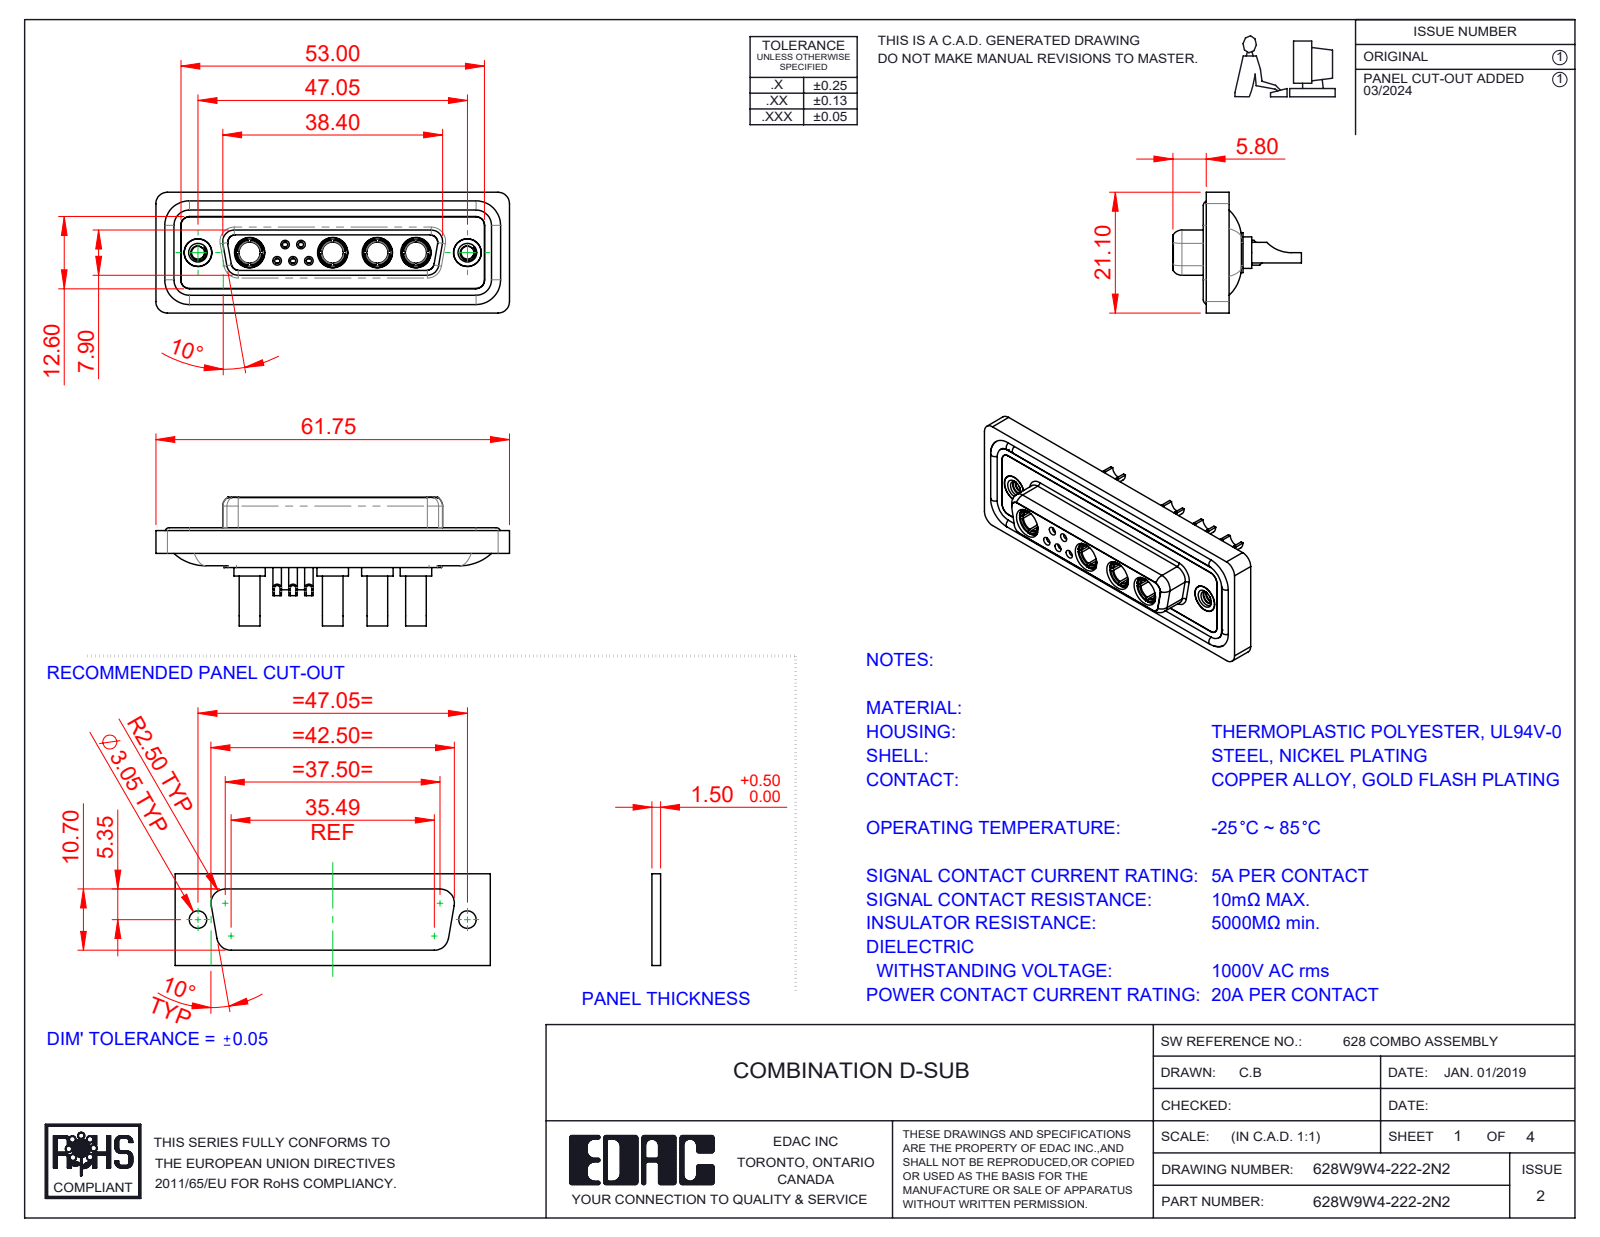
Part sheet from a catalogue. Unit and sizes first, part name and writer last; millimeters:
Units: millimetres
Overall size (bounding box): 61.75 × 22.45 × 21.1
Round holes (diameter × count): ⌀4.85 ×6, ⌀0.9 ×5, ⌀1 ×5, ⌀1.1 ×5, ⌀1.5 ×5, ⌀2 ×5, ⌀2.7 ×4, ⌀3.7 ×4, ⌀5.3 ×4, ⌀1.6 ×3, ⌀1.7 ×2, ⌀2.26 ×2
Round bosses / shafts (diameter × count): ⌀1.6 ×6, ⌀2.2 ×5, ⌀5.5 ×4, ⌀5.2 ×4, ⌀4.96 ×4, ⌀4.75 ×4, ⌀3.75 ×4, ⌀3.6 ×4
Partial cylindrical surfaces — rounded edges, fillets, slot ends (radius × count): R1.5 ×22, R2 ×18, R1.35 ×8, R1.6 ×8, R1 ×6, R0.25 ×4, R0.5 ×4, R0.6 ×4
Main face-to-face distances: 0.4, 1.8, 7.45, 5.65, 0.5, 7.05, 6.6, 1.6, 1.1, 2.9
Hole centre spacings: 3.16, 2.77, 5.03, 2.76, 4.4, 5.02, 5.54, 5.73
Volume: 8 285 mm³ · Surface area: 13 947 mm²
Bodies: 20 solids, 981 faces (318 planar, 397 cylindrical, 266 other)
Part name (STEP PRODUCT): 628Combo Contact Row 1_22; 628W9W4-222-2N2; 628Combo Housing_9W4; 628Combo Shell Rear_25 Contacts (+5 more)
STEP written by: SolidWorks 2023 (CONFIG_CONTROL_DESIGN)
